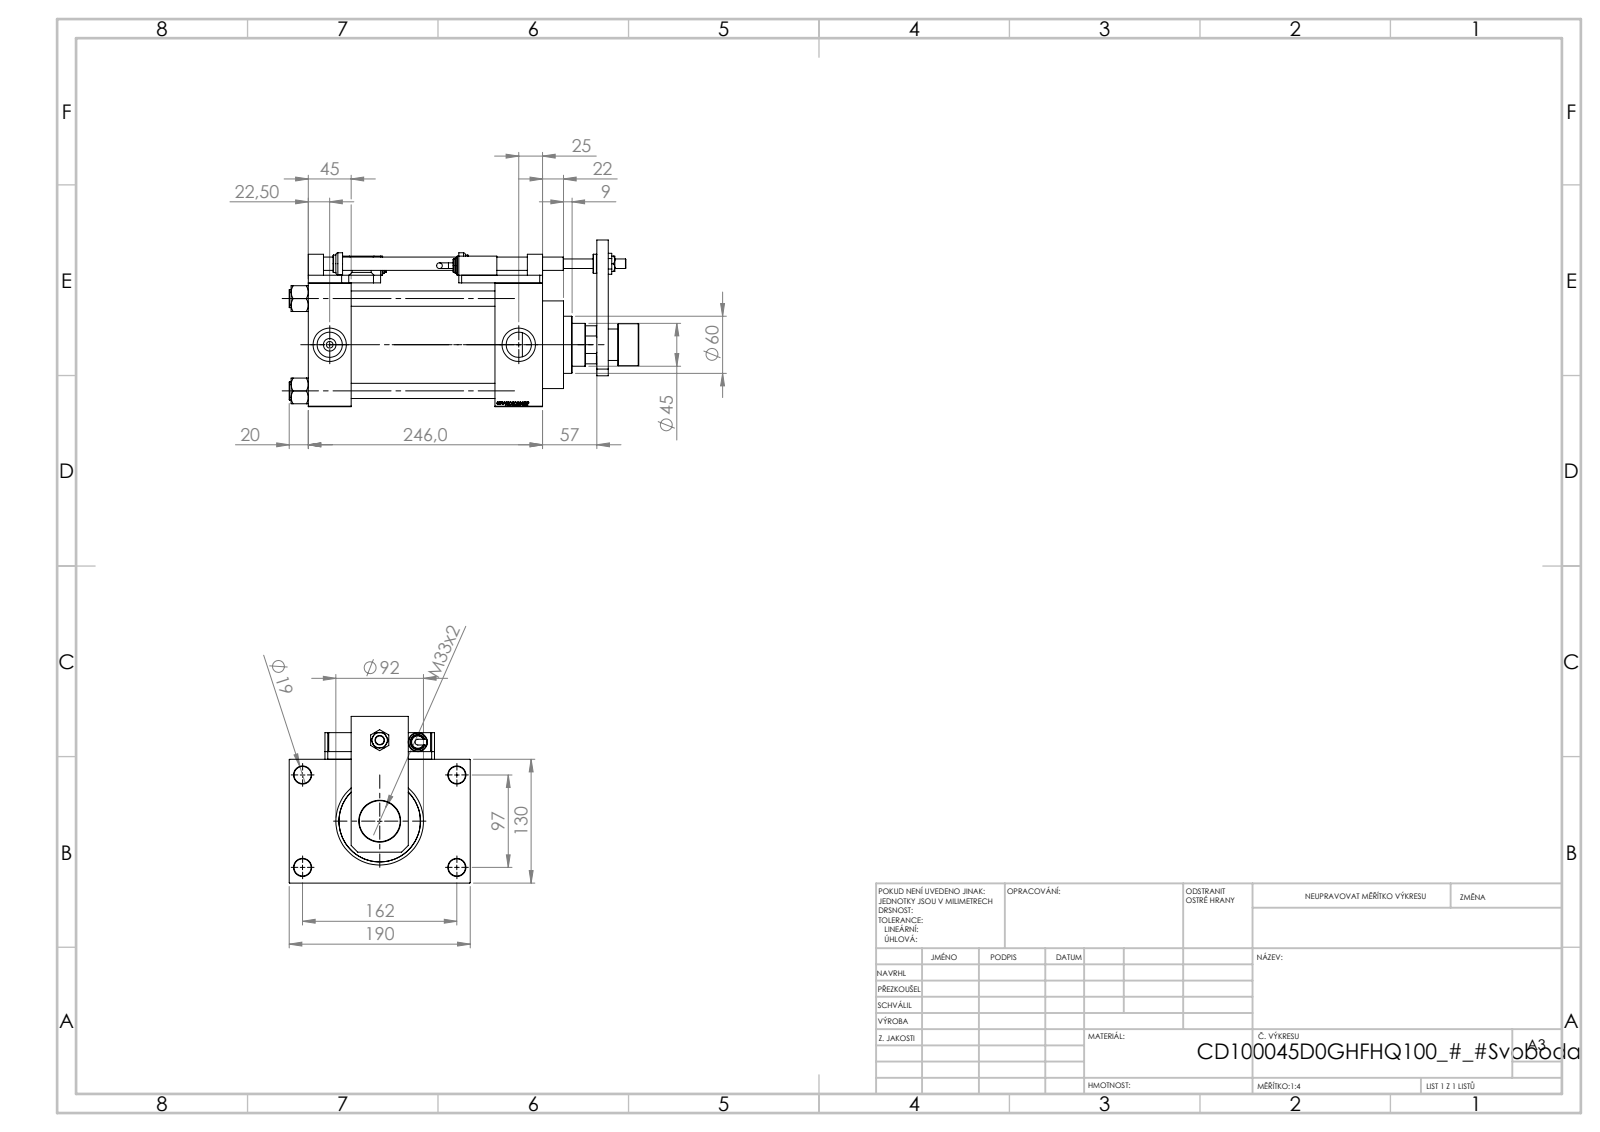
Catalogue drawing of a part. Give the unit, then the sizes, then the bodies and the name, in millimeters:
Units: millimetres
Overall size (bounding box): 367 × 190 × 175
Round holes (diameter × count): ⌀8.5 ×4, ⌀13.5 ×4, ⌀16 ×4, ⌀18 ×4, ⌀7 ×2, ⌀26.44 ×2, ⌀35 ×2, ⌀10 ×1, ⌀14 ×1, ⌀31.5 ×1, ⌀33 ×1, ⌀45 ×1
Round bosses / shafts (diameter × count): ⌀19 ×4, ⌀20 ×3, ⌀16 ×2, ⌀14 ×2, ⌀6 ×2, ⌀106 ×1, ⌀92 ×1, ⌀60 ×1
Partial cylindrical surfaces — rounded edges, fillets, slot ends (radius × count): R7.5 ×4
Main face-to-face distances: 45, 130, 201, 246, 151, 8, 50, 196, 138, 160
Hole centre spacings: 32.55, 68.52, 94.41, 96.9, 102.27, 129.45, 161.73, 32
Volume: 3 253 000 mm³ · Surface area: 543 158 mm²
Bodies: 25 solids, 1392 faces (669 planar, 160 cylindrical, 563 other)
Part name (STEP PRODUCT): V215CD_D_TYCINKA; V215CD_VCP_D; V215CD_SWITCH_Q_TYC; V215CD_SWITCH_Q_MAGNET (+8 more)
STEP written by: SolidWorks 2019 (CONFIG_CONTROL_DESIGN)
